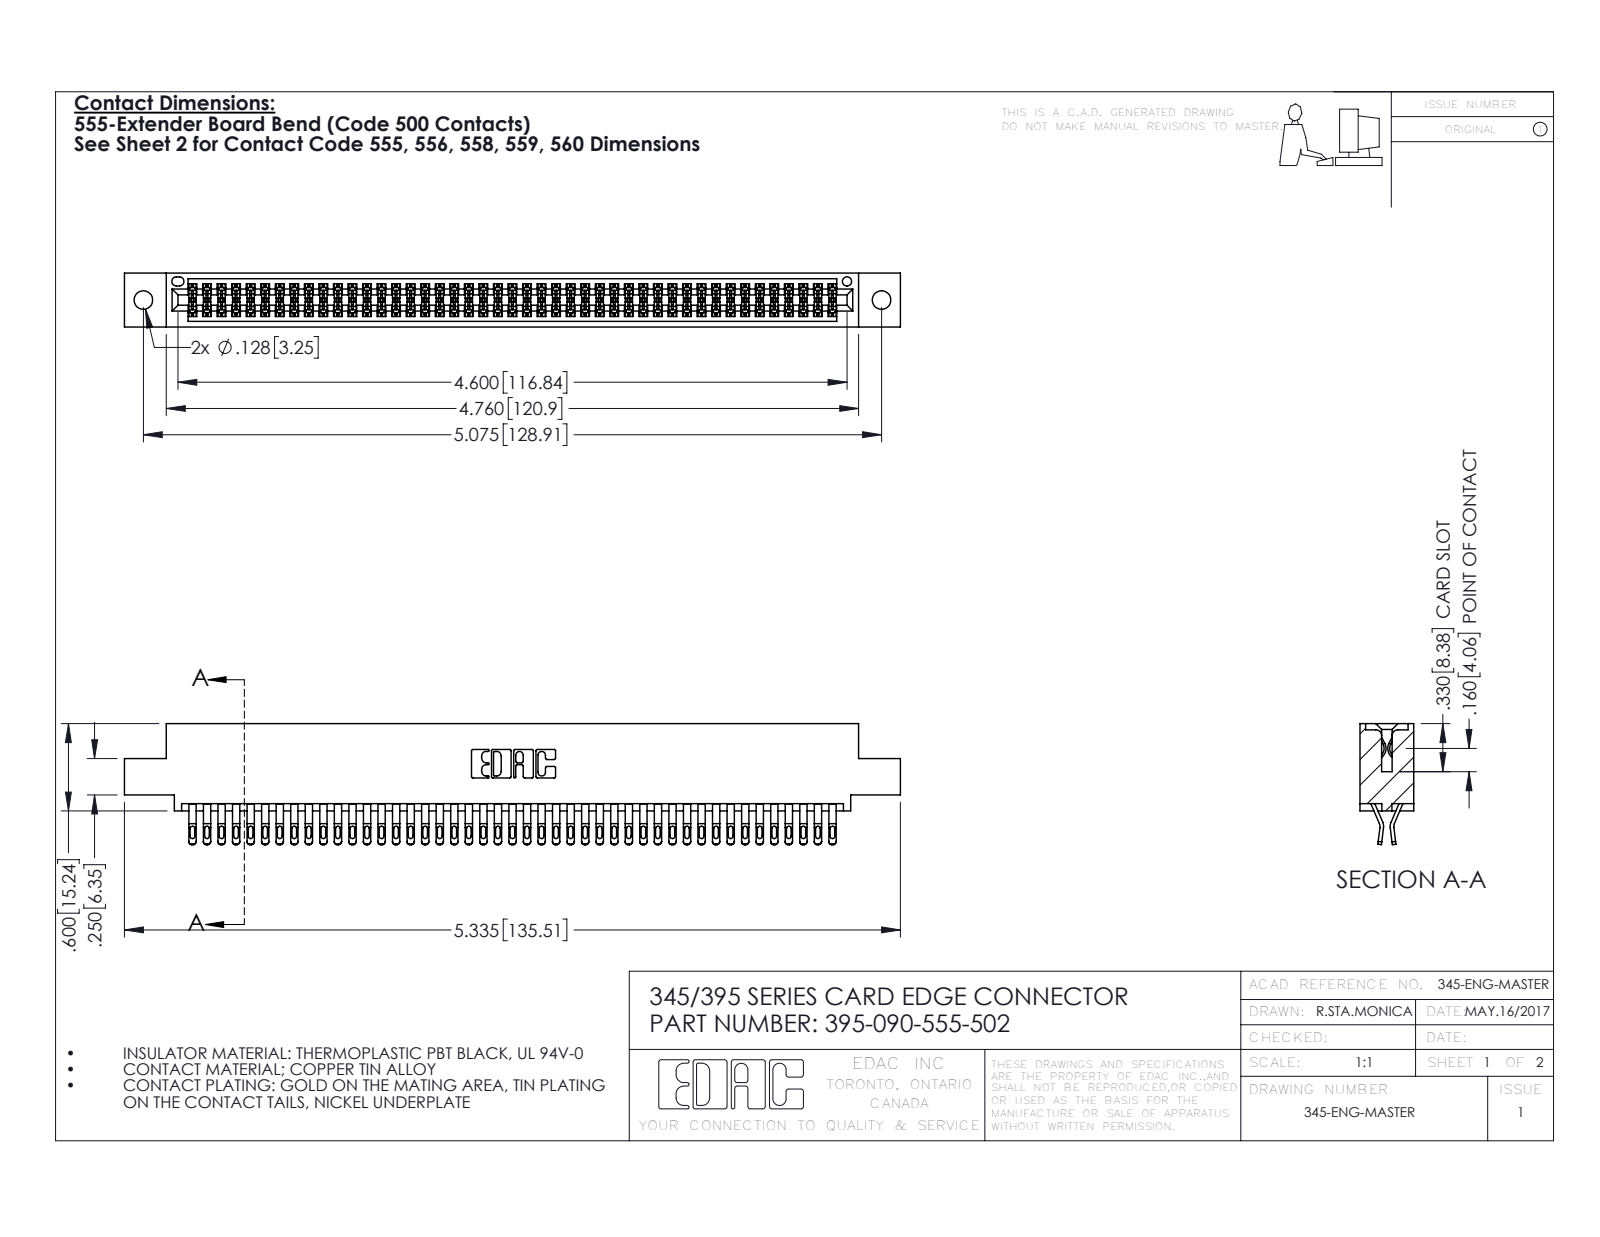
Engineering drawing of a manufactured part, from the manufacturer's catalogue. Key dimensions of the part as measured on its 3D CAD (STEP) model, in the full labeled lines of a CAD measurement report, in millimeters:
Part name (STEP PRODUCT): 395-090-555-502; 345 Part_0.110 Offset - 0.128 Dia; 345-292-001_555 Tail
STEP written by: SolidWorks 2016 (CONFIG_CONTROL_DESIGN)
Units: millimetres
Bodies: 91 solids, 5170 faces (2874 planar, 2296 cylindrical, 0 other)
Overall size (bounding box): 135.5 × 21.1 × 9.4
Volume: 13 300 mm³ · Surface area: 20 510 mm²
Round holes (diameter × count): ⌀3.3 ×2, ⌀1.6 ×1
Partial cylindrical surfaces — rounded edges, fillets, slot ends (radius × count): R0.4 ×225, R0.5 ×180, R0.2 ×135, R0.3 ×22, R0.2 ×6, R0.8 ×6, R0.7 ×3, R0.3 ×2
Main face-to-face distances: 7.6, 1.8, 0.6, 9.4, 5.1, 2.5, 6.9, 5.7, 4.4, 3.8
Hole centre spacings: 6.9, 122.9, 128.9
